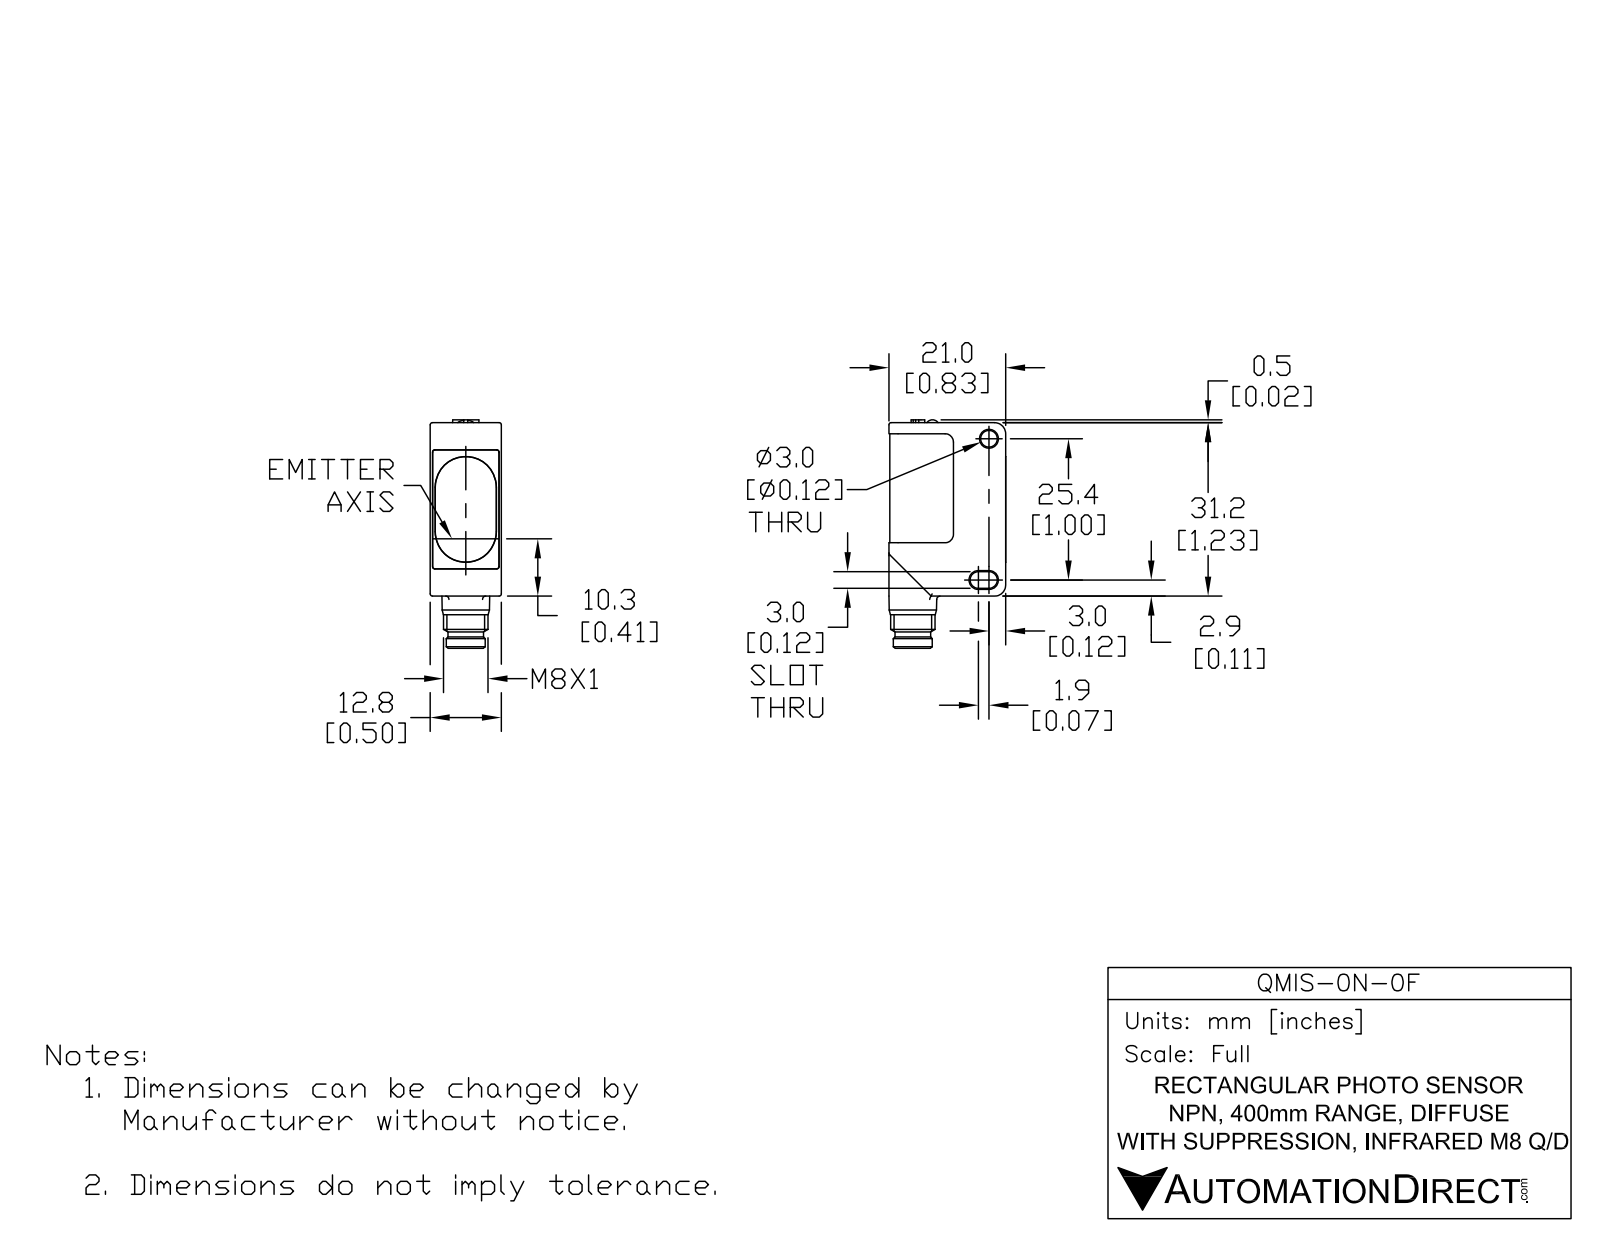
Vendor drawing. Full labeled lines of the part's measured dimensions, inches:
Part name (STEP PRODUCT): QMIS-0N-0F
STEP written by: SolidWorks 2017 (AUTOMOTIVE_DESIGN)
Units: inches
Bodies: 7 solids, 262 faces (123 planar, 92 cylindrical, 47 other)
Overall size (bounding box): 1.618 × 0.827 × 0.504
Volume: 0.468 in³ · Surface area: 7.721 in²
Round holes (diameter × count): ⌀0.118 ×1, ⌀0.173 ×1, ⌀0.228 ×1
Round bosses / shafts (diameter × count): ⌀0.039 ×4, ⌀0.315 ×1, ⌀0.276 ×1, ⌀0.252 ×1, ⌀0.122 ×1, ⌀0.11 ×1
Partial cylindrical surfaces — rounded edges, fillets, slot ends (radius × count): R0.016 ×10, R0.059 ×7, R0.024 ×4, R0.039 ×4, R0.177 ×4, R0.02 ×3, R0.065 ×2, R0.079 ×2
Main face-to-face distances: 0.498, 0.504, 0.02, 0.11, 0.039, 0.016, 0.071, 0.492, 0.488, 0.482
Hole centre spacings: 0.311
